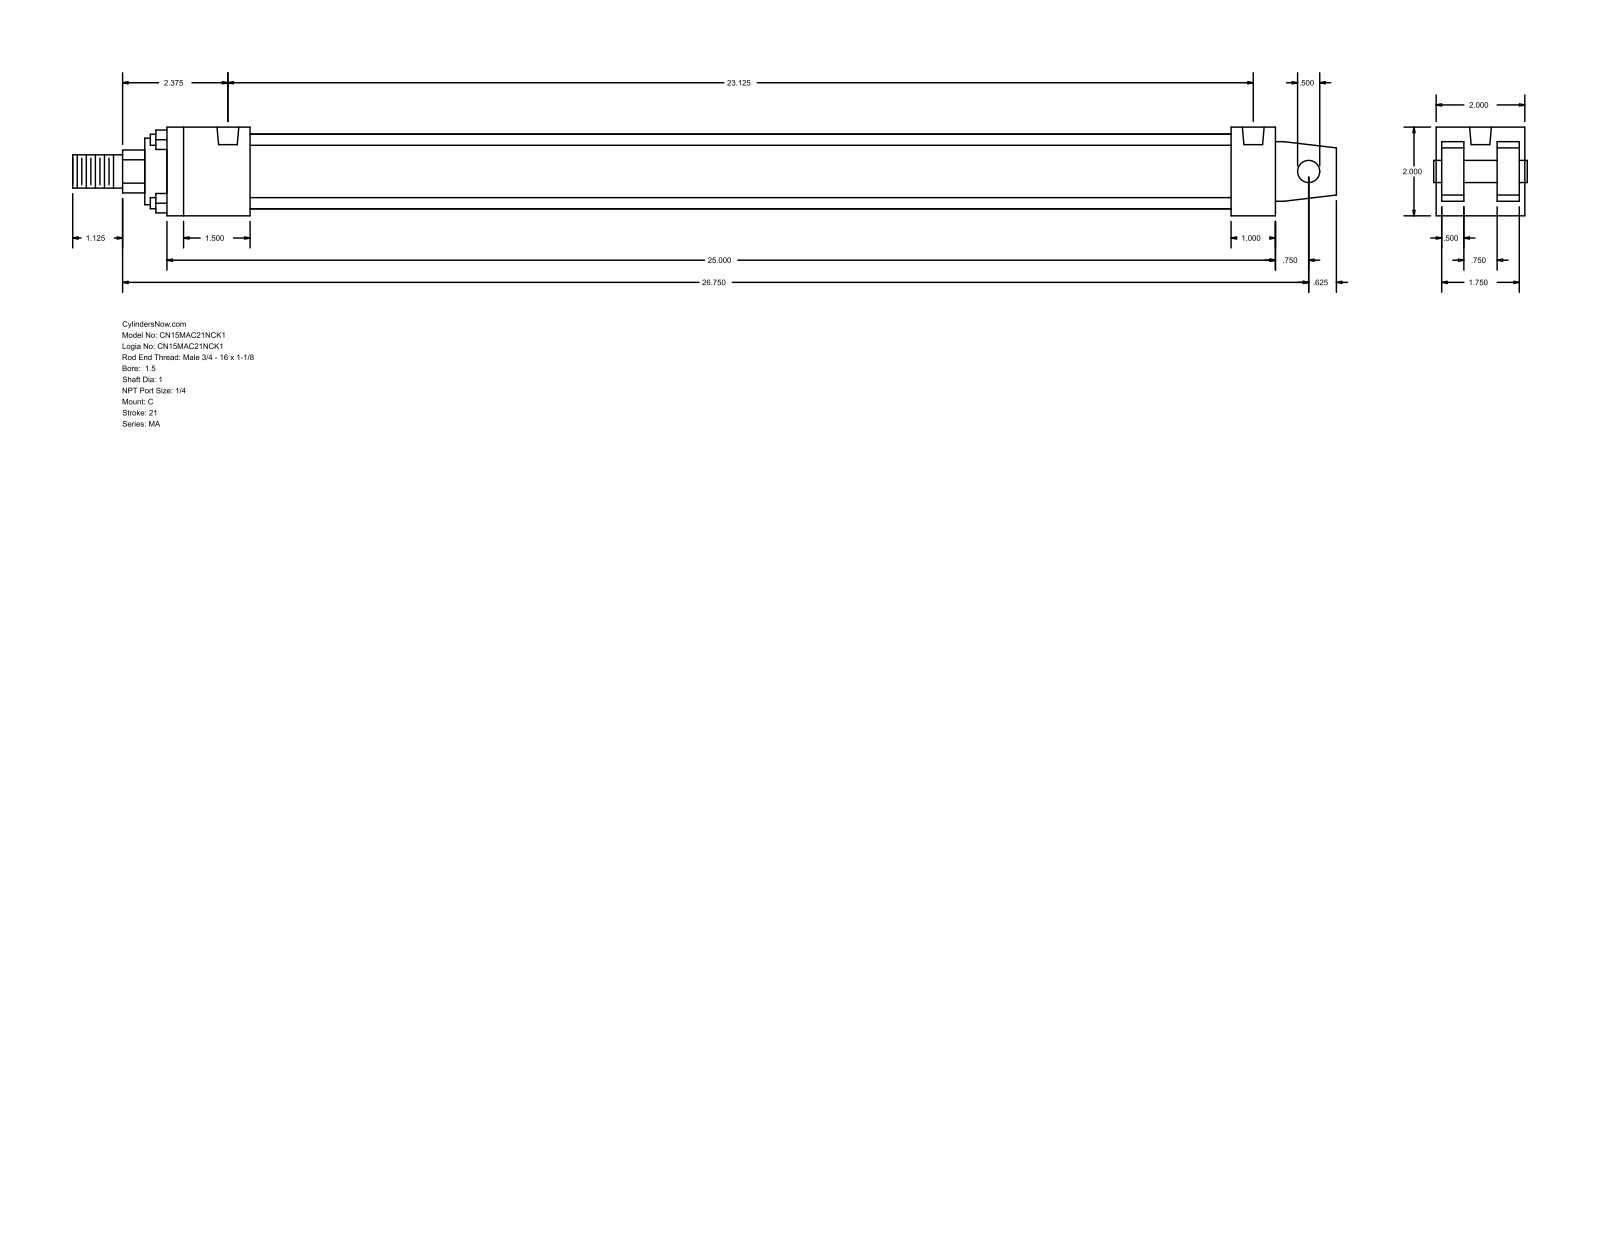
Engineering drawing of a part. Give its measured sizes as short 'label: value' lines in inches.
name: MA_C__0150_1
written by: GSSL Pune (CONFIG_CONTROL_DESIGN)
unit: in
bodies: 0 solids, 103 faces (76 planar, 27 cylindrical, 0 other)
size: 28.5 × 2 × 2
holes: 4× ⌀0.313, 2× ⌀0.492
bosses: 4× ⌀0.25, 1× ⌀1.69, 1× ⌀1.5, 1× ⌀1, 1× ⌀0.75, 1× ⌀0.5
rounds: 1× R0.484
face distances: 2, 1.875, 0.5, 1.375, 0.125, 0.625, 1.25, 2.375, 24.5, 25
hole spacings: 23.125
